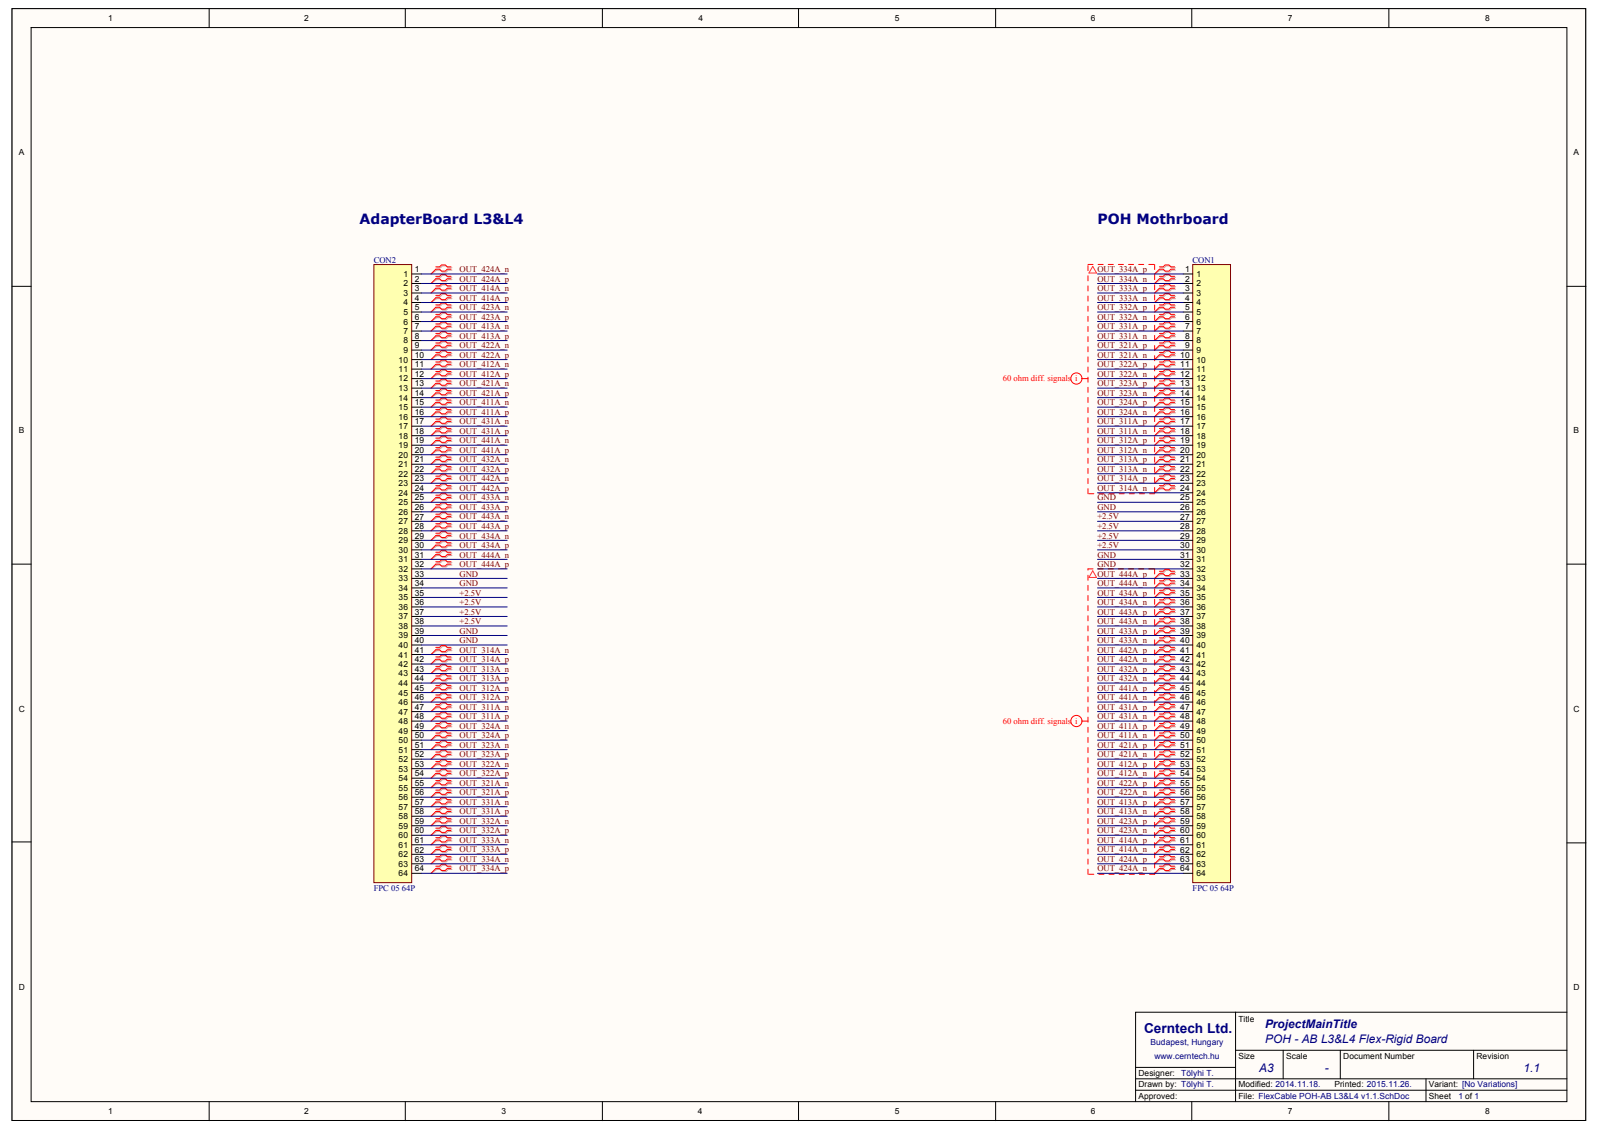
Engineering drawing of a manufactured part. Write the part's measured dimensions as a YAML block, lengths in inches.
part_name: "PCB; BoardFC_POH_L3&L4_v1.1.3"
step_written_by: "Open CASCADE 6.5 (AUTOMOTIVE_DESIGN)"
units: inches
bodies: {solids: 1, faces: 84, planar: 84, cylindrical: 0, other: 0}
overall_size: [1.772, 1.323, 0.012]
volume: 0.027
surface_area: 4.613
face_to_face_distances: [1.28, 1.772, 0.022, 1.301, 1.268, 1.271, 2.07, 2.072, 1.336, 1.323]
